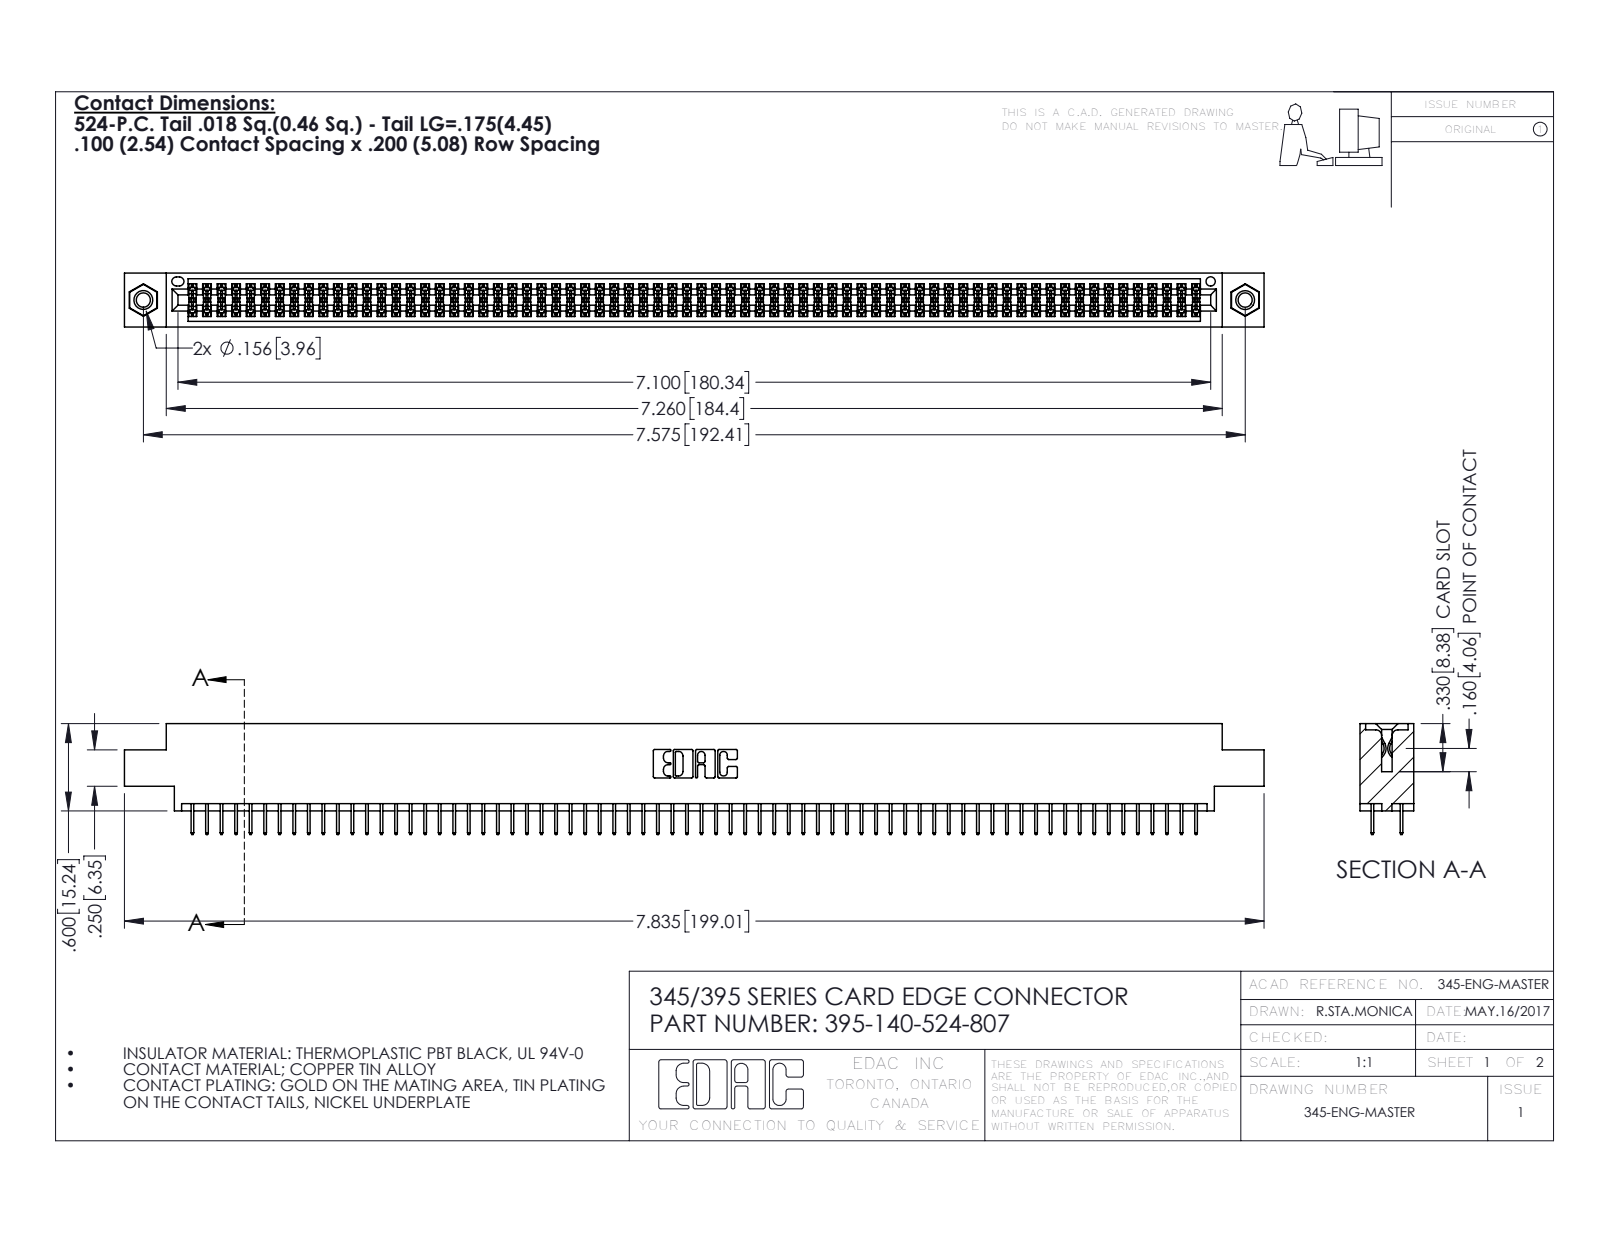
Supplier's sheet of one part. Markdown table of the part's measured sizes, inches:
| quantity | value |
| --- | --- |
| part name | 345-292-001_345-293-124; 345 Part_0.170 Offset - 0.156 Dia-TI; 395-140-524-807; 345-250-001_345-250-005-103 |
| STEP written by | SolidWorks 2016 (CONFIG_CONTROL_DESIGN) |
| units | inches |
| bodies | 143 solids, 7750 faces (5576 planar, 2158 cylindrical, 16 other) |
| overall size | 7.835 × 0.762 × 0.37 |
| volume | 1.175 in³ |
| surface area | 44.35 in² |
| round holes (diameter × count) | 0.098 × 2, 0.125 × 2, 0.156 × 2, 0.064 × 1 |
| round bosses / shafts (diameter × count) | 0.155 × 2 |
| partial cylindrical surfaces (radius × count) | 0.006 × 210, 0.01 × 22, 0.007 × 6, 0.031 × 6, 0.026 × 3, 0.014 × 2, 0.019 × 2, 0.022 × 2 |
| main face-to-face distances | 0.072, 0.298, 0.2, 0.37, 0.098, 0.272, 0.025, 0.225, 0.072, 0.175 |
| hole center spacings | 0.27, 7.339, 7.575 |
